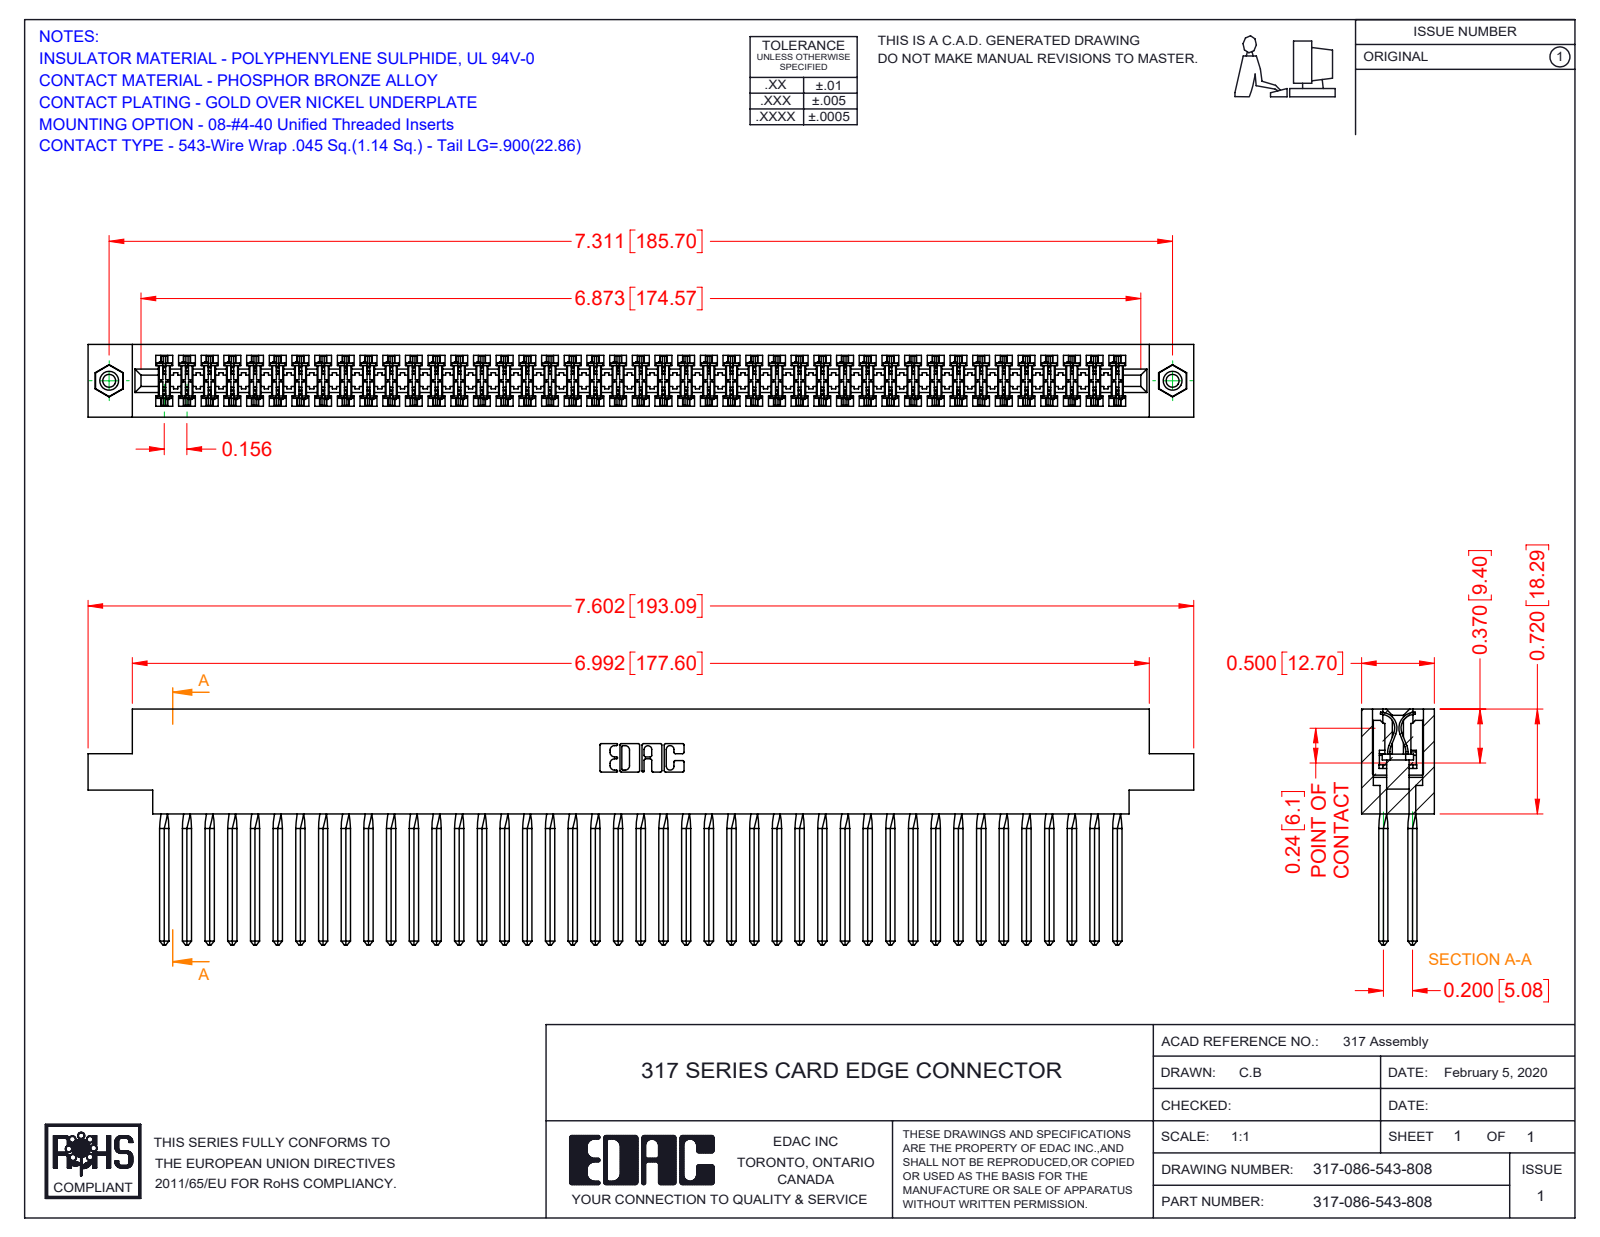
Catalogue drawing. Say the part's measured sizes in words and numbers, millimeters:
The part is named "317 Part_.156 Dia - TI; 345-250-001_345-250-003-102; 317-086-543-808; 317-290-001_543". Its 3-D file was written by "SolidWorks 2016 (CONFIG_CONTROL_DESIGN)". It is 89 solids with 7816 faces: 6368 planar, 1088 cylindrical and 360 other. Overall it measures 193.1 by 41.1 by 12.7 millimeters. Its volume is 32 860 cubic millimeters and its surface area 49 920 square millimeters. Round holes: 2 of diameter 2.3, 2 of diameter 3.2, 2 of diameter 4. Round bosses or shafts: 2 of diameter 3.9. Partial cylindrical surfaces (rounded edges, fillets, slot ends): 172 of radius 0.4, 22 of radius 0.3, 6 of radius 0.2, 6 of radius 0.8, 3 of radius 0.7, 2 of radius 2.4, 2 of radius 2.5, 2 of radius 2.8. The main face-to-face distances are 12.7, 1.9, 10.8, 8.9, 5, 2.8, 2.4, 5.1, 2.9, 3.3. The hole center spacings are 185.7.
